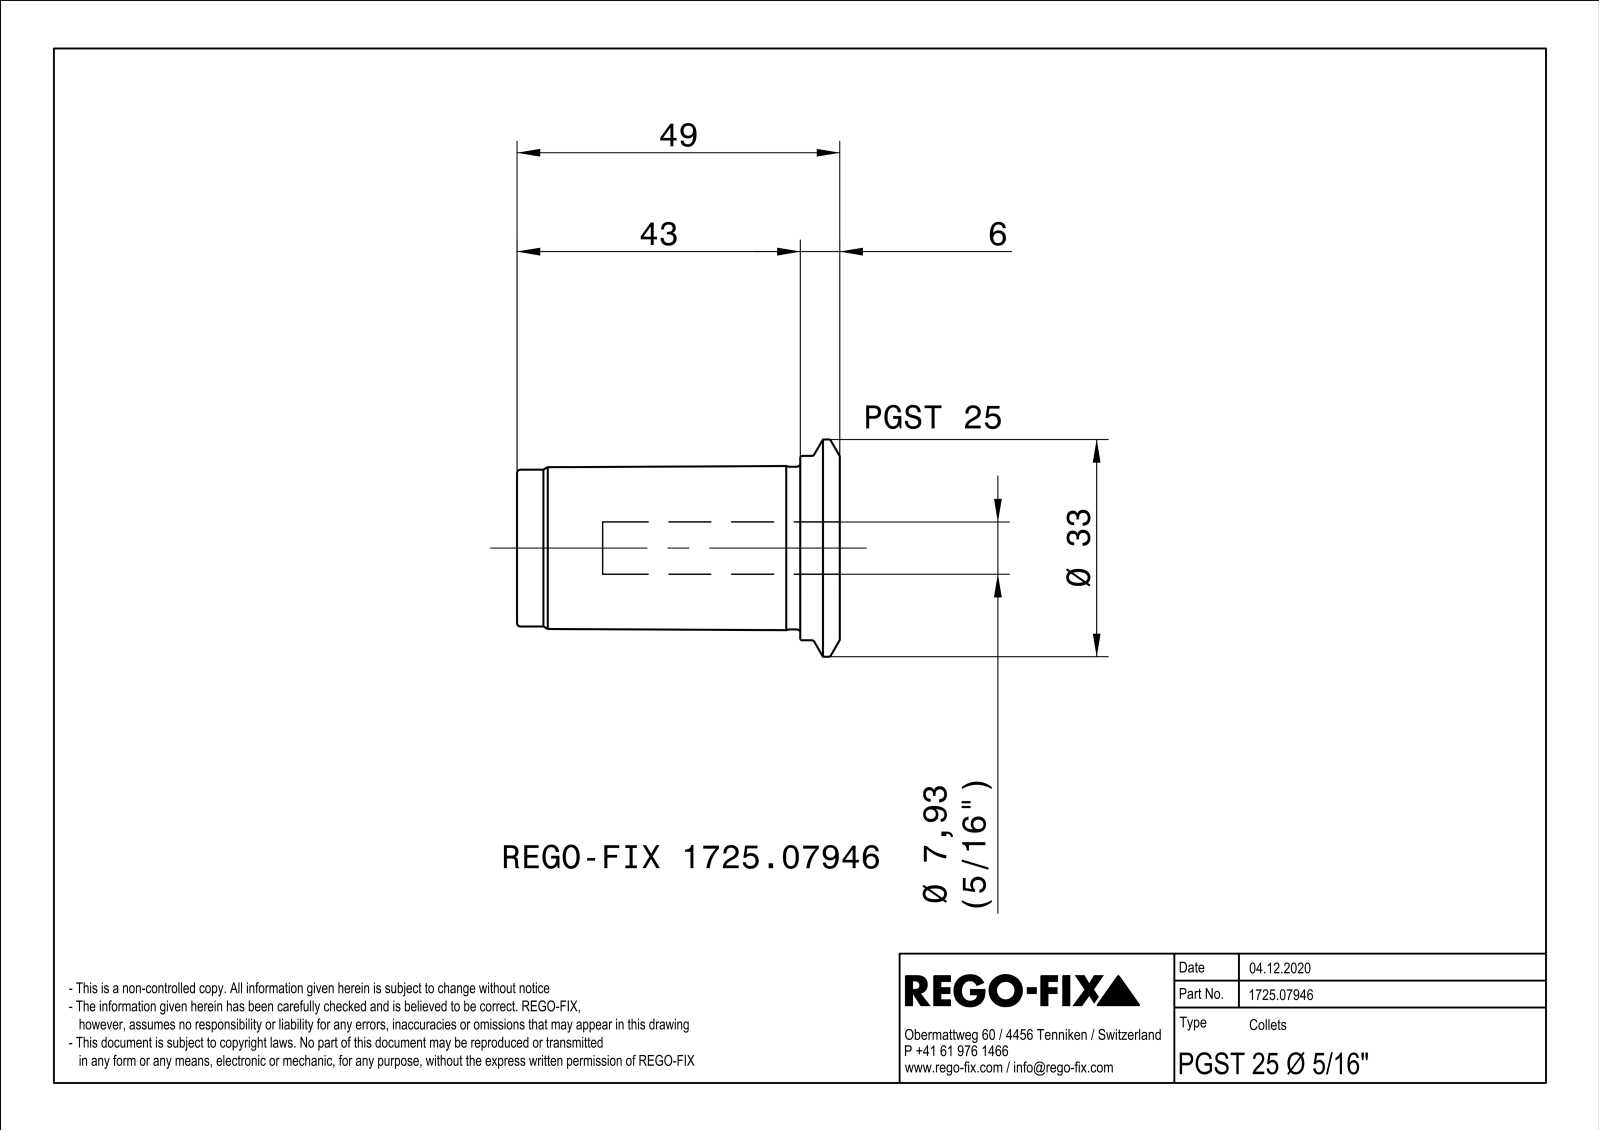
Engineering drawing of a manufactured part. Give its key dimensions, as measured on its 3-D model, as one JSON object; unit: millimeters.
{"part_name": "NOCUT", "step_written_by": "SIEMENS PLM Software Solid Edge ST10 (AUTOMOTIVE_DESIGN)", "units": "millimeters", "bodies": {"solids": 2, "faces": 52, "planar": 12, "cylindrical": 18, "other": 22}, "overall_size": [49, 32.98, 32.98], "volume_mm3": 21833, "surface_area_mm2": 8168, "round_holes": [[3, 4], [7.93, 1], [10, 1], [17, 1], [21.19, 1], [22.3, 1]], "round_bosses_or_shafts": [[32.98, 1], [28, 1], [24.7, 1], [23.8, 1], [22, 1], [21, 1], [5, 1]], "partial_cylinders_radius": [[1, 1]], "face_to_face_distances": [43.5, 49, 5.5, 6, 37.5, 43, 36, 30, 7.5, 13], "hole_center_spacings": [6, 10.39, 10.4]}
